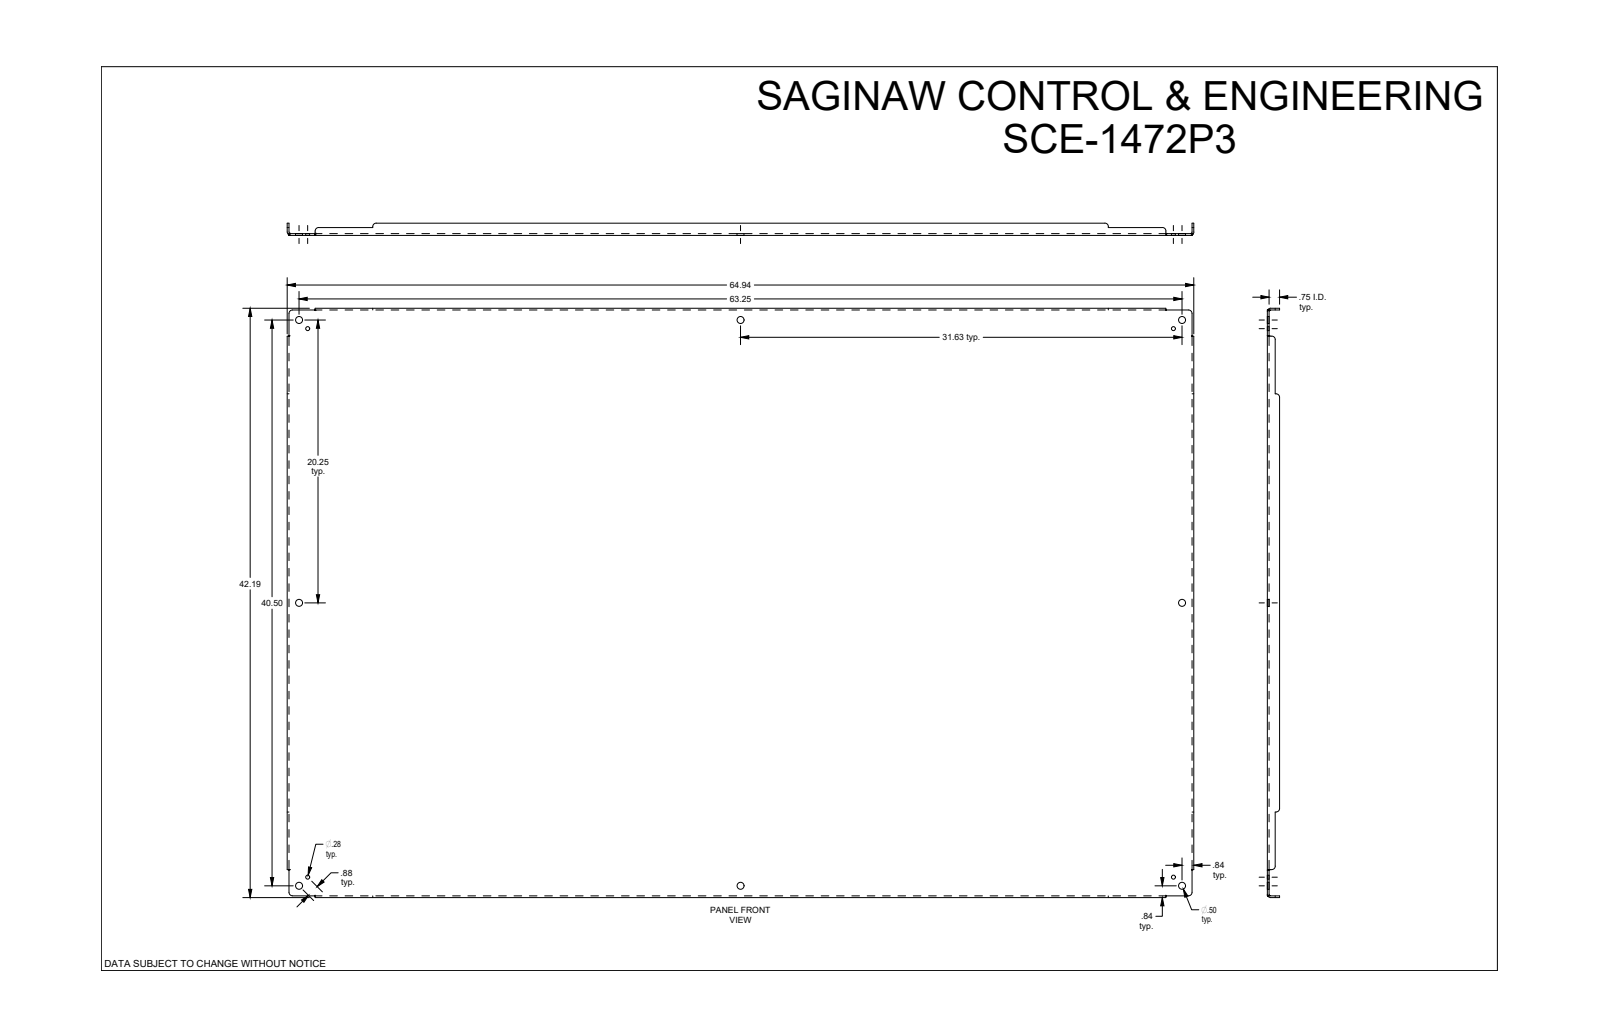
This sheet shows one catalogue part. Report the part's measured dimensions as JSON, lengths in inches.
{"part_name": "SCE-1472P3", "step_written_by": "SolidWorks 2019 (CONFIG_CONTROL_DESIGN)", "units": "inches", "bodies": {"solids": 1, "faces": 110, "planar": 46, "cylindrical": 40, "other": 24}, "overall_size": [64.938, 42.188, 0.875], "volume_in3": 357.4, "surface_area_in2": 5747, "round_holes": [[0.5, 8], [0.281, 4]], "partial_cylinders_radius": [[0.25, 12], [0.112, 4], [0.237, 4]], "face_to_face_distances": [0.125, 42.063, 0.125, 64.813, 41.938, 42.187, 64.687, 64.938, 0.75, 0.875], "hole_center_spacings": [0.875, 19.641, 20.25, 31.013, 31.625, 37.552, 39.886, 50.516]}
